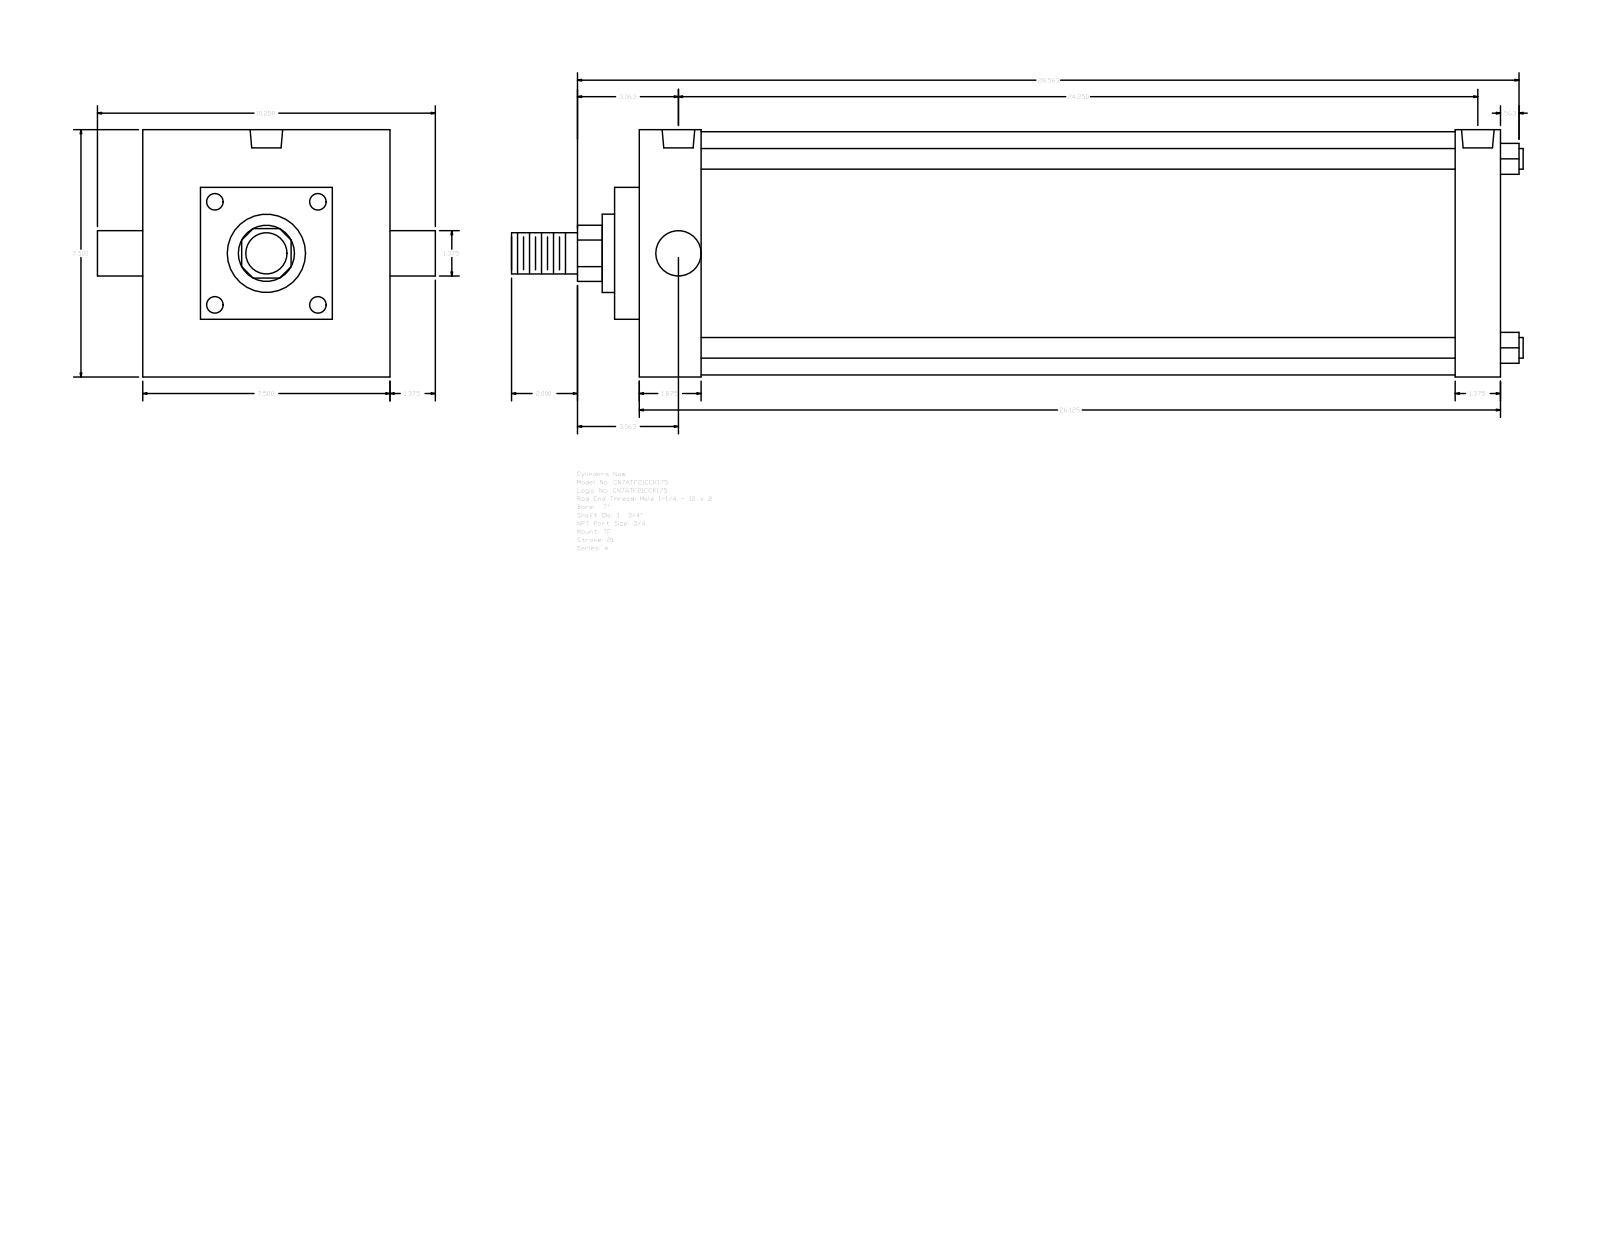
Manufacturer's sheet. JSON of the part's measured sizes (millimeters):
{"part_name": "A_TF__0700_1.75", "step_written_by": "GSSL Pune (CONFIG_CONTROL_DESIGN)", "units": "millimeters", "bodies": {"solids": 0, "faces": 89, "planar": 65, "cylindrical": 24, "other": 0}, "overall_size": [779.46, 260.35, 190.5], "round_holes": [[15.08, 3], [25.12, 2]], "round_bosses_or_shafts": [[15.88, 4], [187.32, 1], [60.33, 1], [44.45, 1], [34.92, 1], [31.75, 1]], "partial_cylinders_radius": [[21.63, 1]], "face_to_face_distances": [190.5, 663.58, 34.93, 146.05, 19.05, 47.63, 615.95, 628.65, 581.02, 44.45], "hole_center_spacings": [5.56, 610.39, 604.83, 615.95]}
